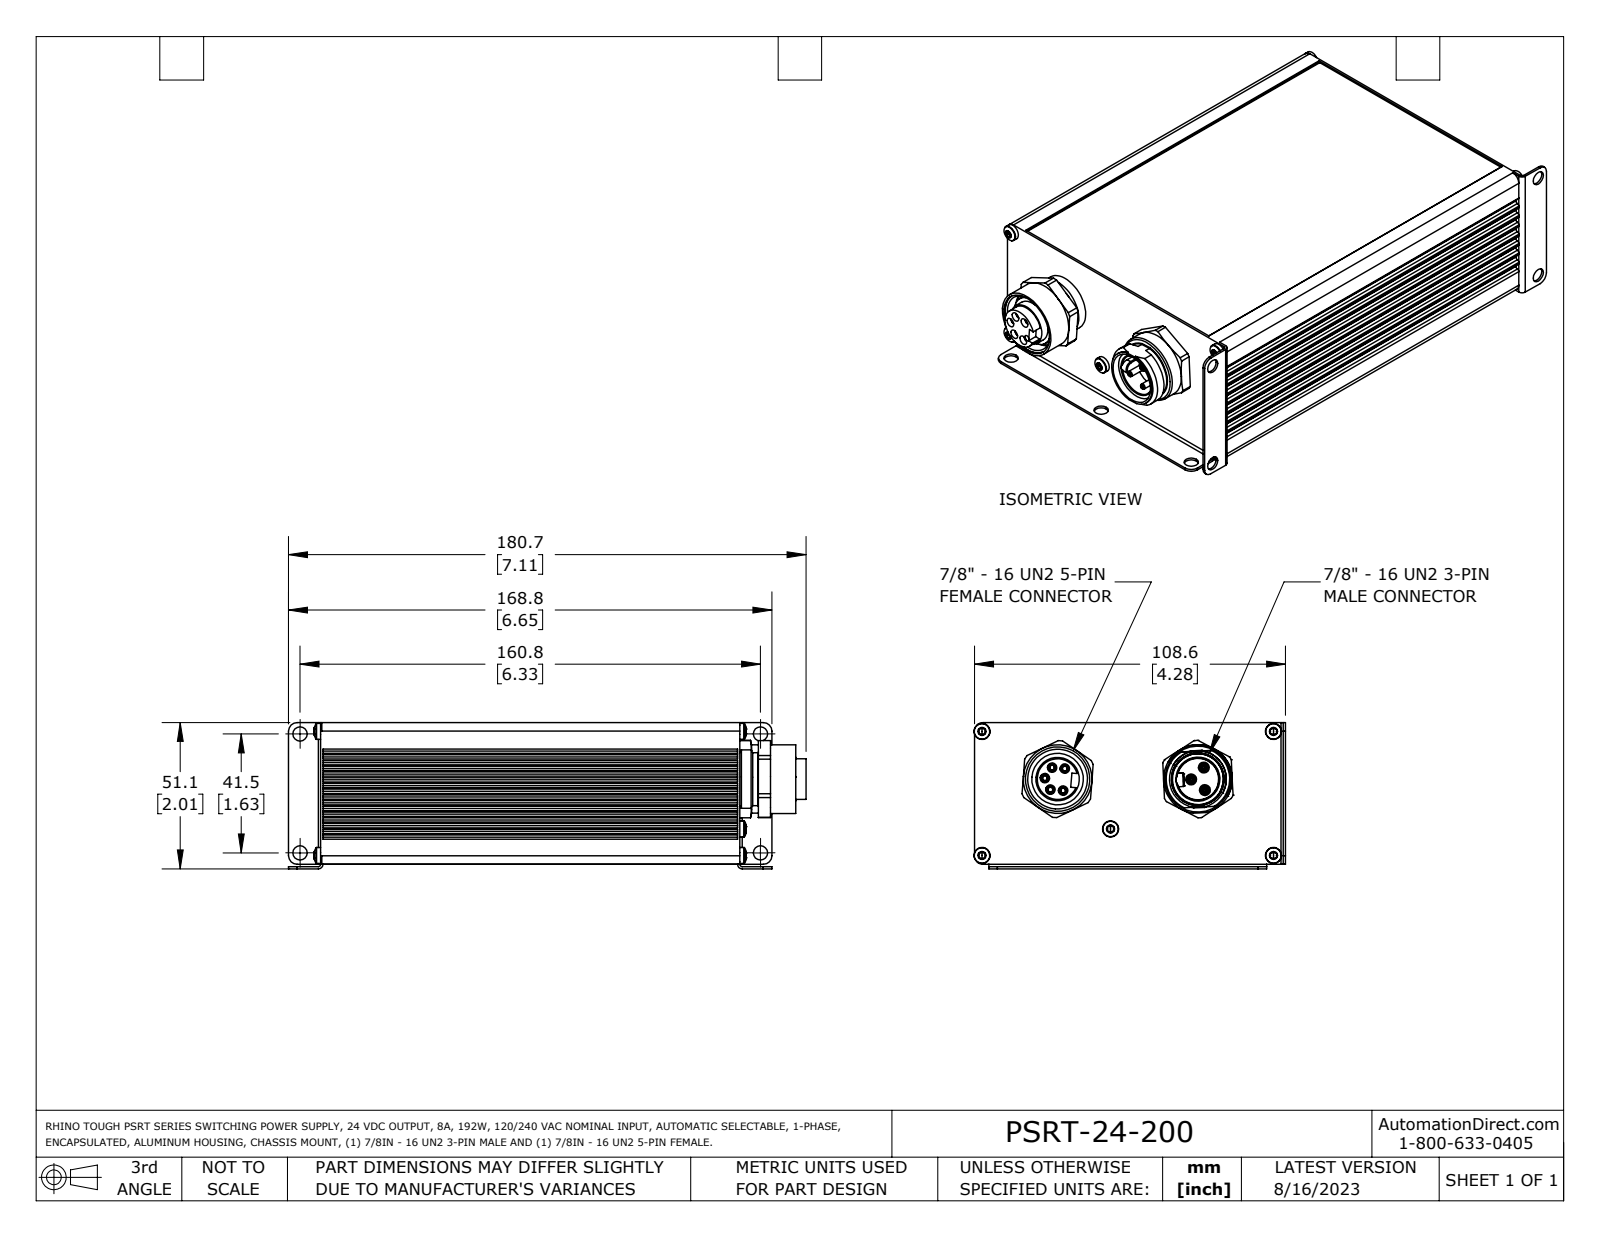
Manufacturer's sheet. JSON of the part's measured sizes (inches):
{"part_name": "PSRT-24-200_REV1", "step_written_by": "SolidWorks 2021 (AUTOMOTIVE_DESIGN)", "units": "inches", "bodies": {"solids": 1, "faces": 597, "planar": 221, "cylindrical": 276, "other": 100}, "overall_size": [7.114, 4.283, 2.012], "volume_in3": 47.36, "surface_area_in2": 115.6, "round_holes": [[0.197, 10], [0.083, 5], [0.13, 5], [0.134, 5], [0.63, 1], [0.728, 1], [0.821, 1], [0.886, 1], [0.921, 1]], "round_bosses_or_shafts": [[0.22, 5], [0.118, 3], [0.079, 3], [0.945, 2], [0.803, 1], [0.783, 1], [0.748, 1], [0.728, 1]], "partial_cylinders_radius": [[0.03, 64], [0.01, 30], [0.025, 30], [0.118, 12], [0.008, 6], [0.031, 4], [0.063, 4], [0.012, 2]], "face_to_face_distances": [1.929, 0.031, 5.764, 0.063, 4.213, 1.961, 1.992, 0.02, 2.012, 1.98], "hole_center_spacings": [0.175, 6.331, 1.752, 6.569, 0.175, 0.303, 0.304, 0.35]}
